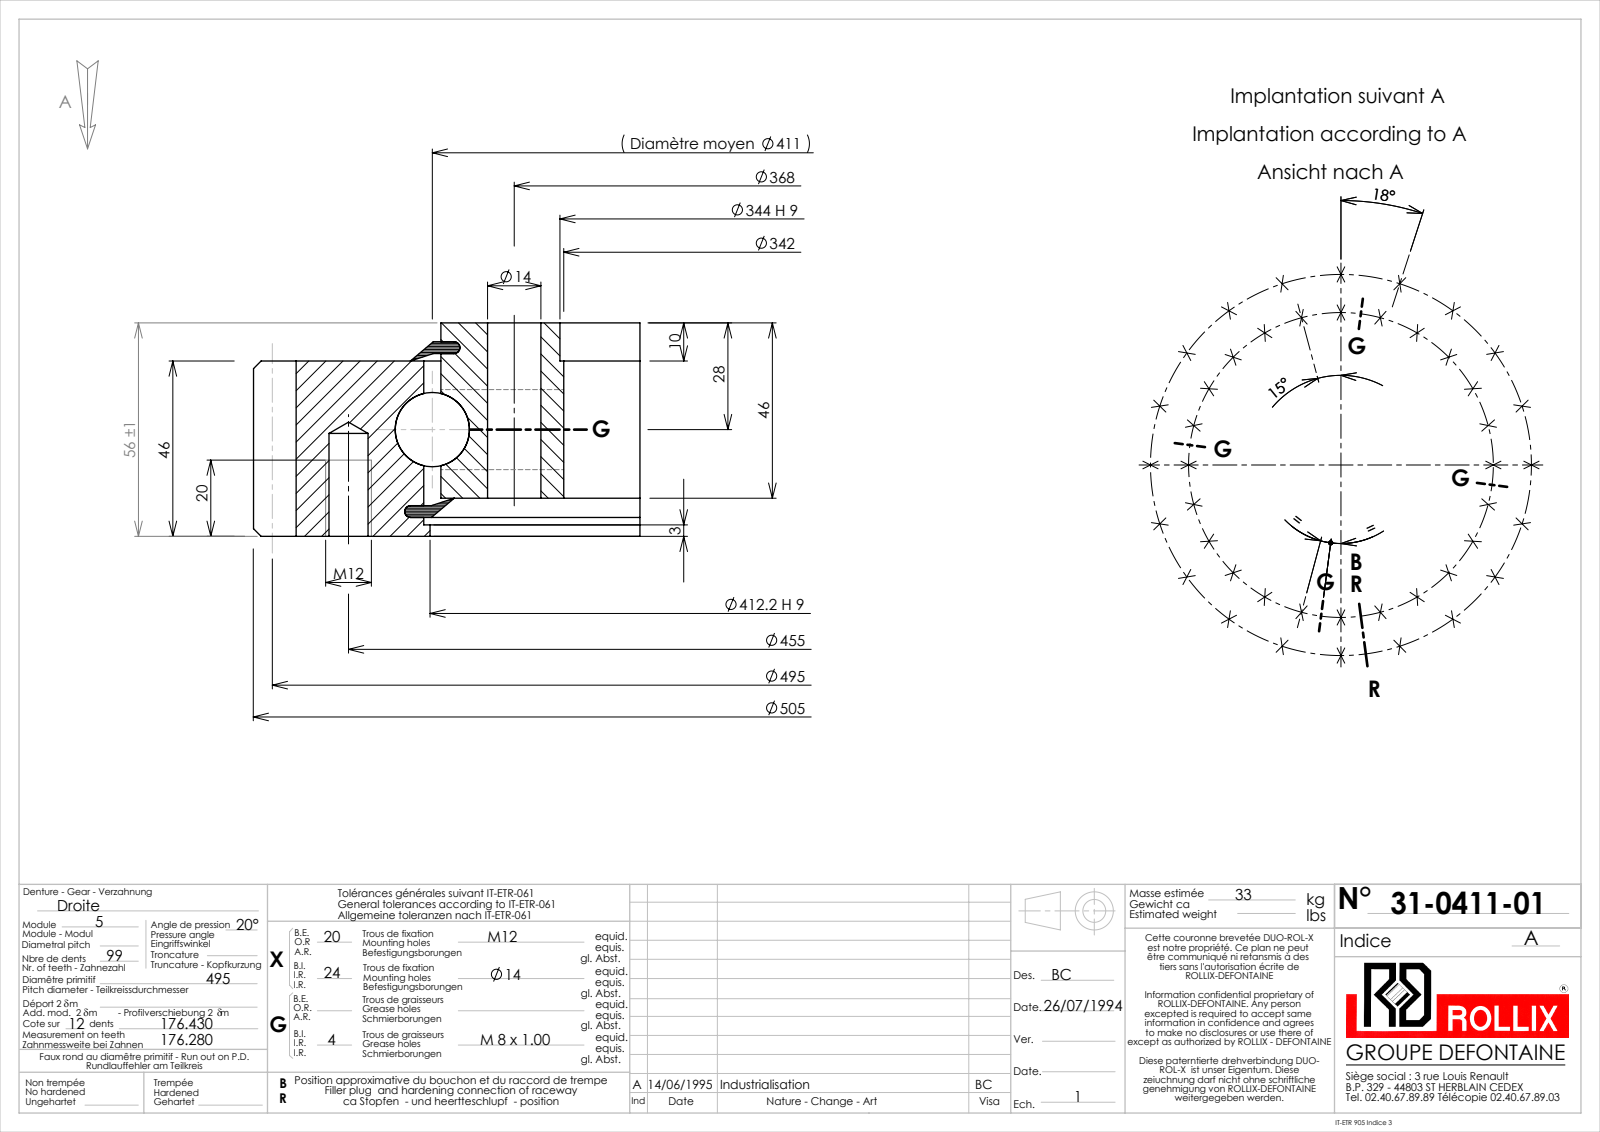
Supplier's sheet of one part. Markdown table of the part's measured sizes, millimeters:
| quantity | value |
| --- | --- |
| part name | 31-0411-01 |
| STEP written by | SolidWorks 2016 (CONFIG_CONTROL_DESIGN) |
| units | millimeters |
| bodies | 9 solids, 880 faces (252 planar, 321 cylindrical, 307 other) |
| overall size | 504.99 × 504.94 × 56 |
| volume | 3 888 000 mm³ |
| surface area | 685 646 mm² |
| round holes (diameter × count) | 14 × 24, 10.25 × 20, 7 × 4, 342 × 1, 344 × 1, 412.2 × 1, 415.5 × 1 |
| round bosses / shafts (diameter × count) | 8 × 4, 406.5 × 1 |
| partial cylindrical surfaces (radius × count) | 241.25 × 1, 252.5 × 1 |
| main face-to-face distances | 46, 10, 36, 56, 5.05, 1.95, 43, 4.95, 51.05, 41.05 |
| hole center spacings | 71.18, 227.5, 405.41, 206.56, 432.73, 449.4, 184, 140.6 |
